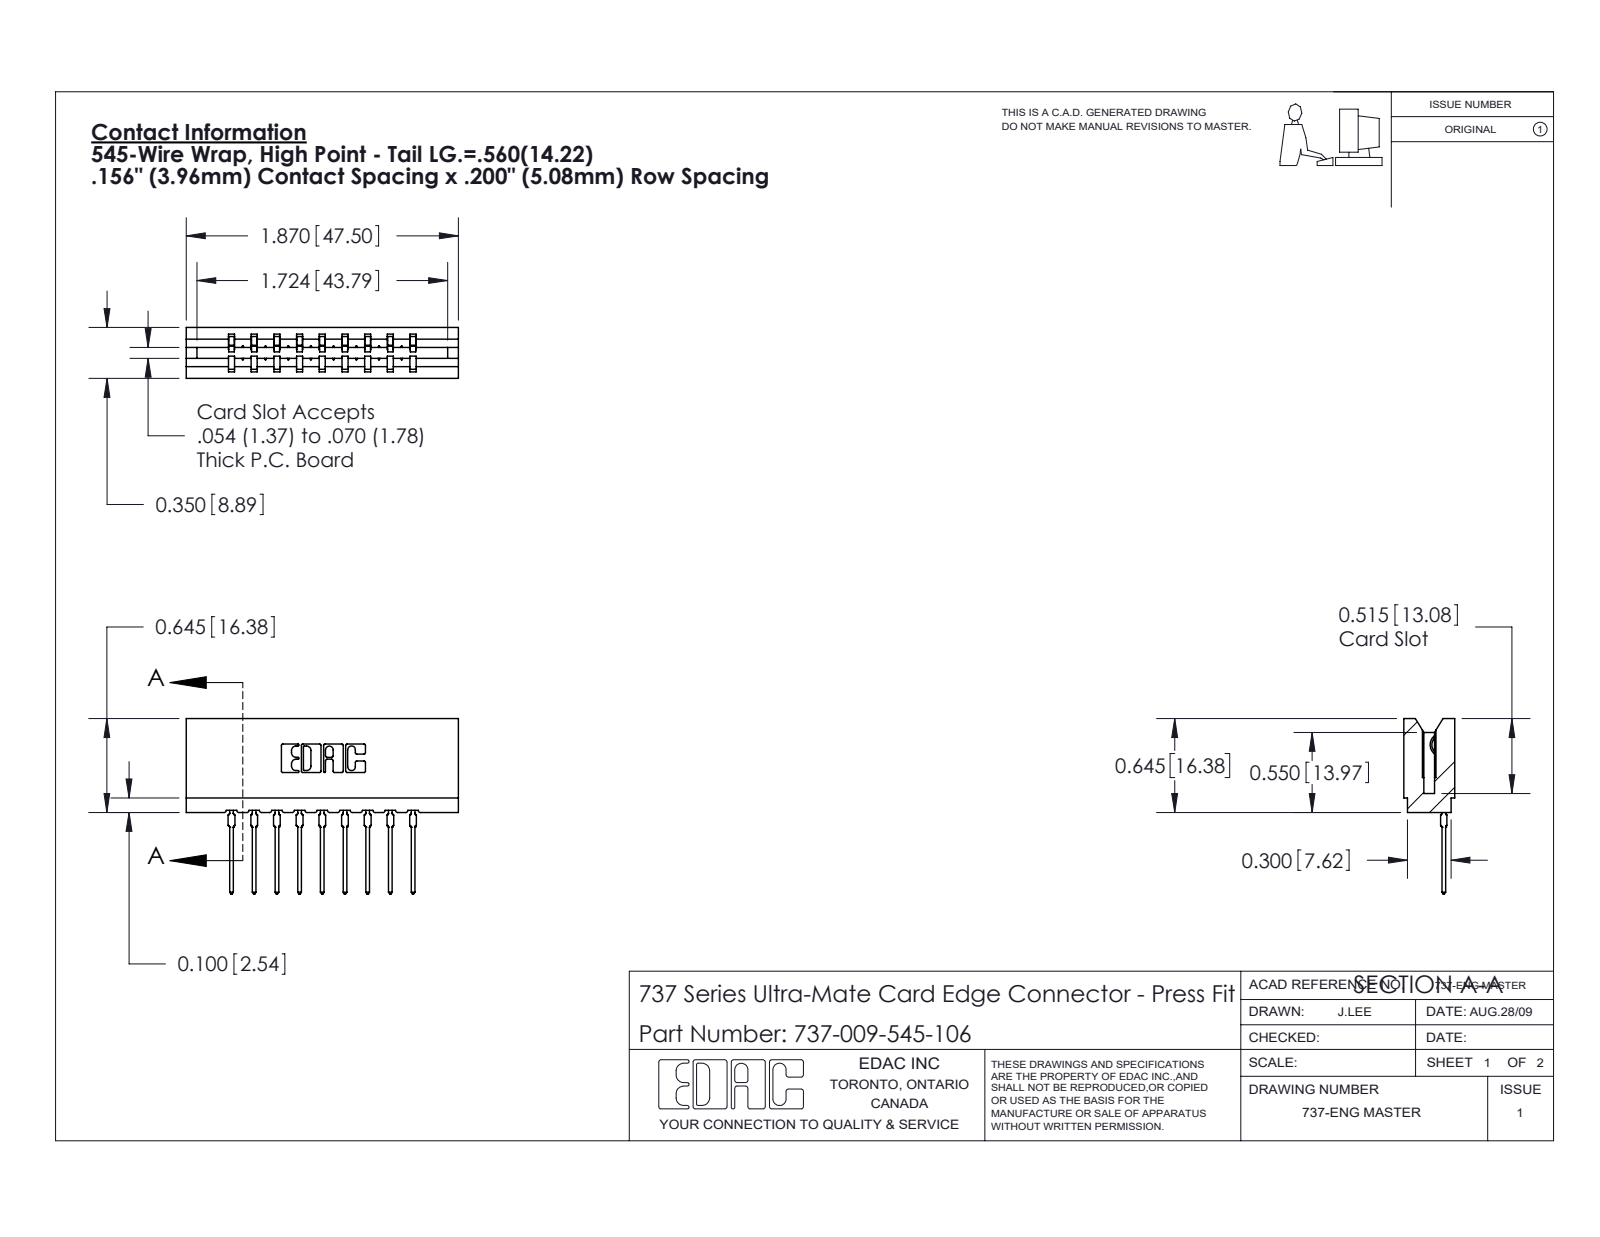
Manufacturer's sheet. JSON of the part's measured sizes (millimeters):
{"part_name": "745-292-001_545; 737 Part_Insulator Option - 06; 737-009-545-106", "step_written_by": "SolidWorks 2020 (CONFIG_CONTROL_DESIGN)", "units": "millimeters", "bodies": {"solids": 10, "faces": 1112, "planar": 667, "cylindrical": 211, "other": 234}, "overall_size": [47.5, 30.6, 8.9], "volume_mm3": 4830, "surface_area_mm2": 6027, "partial_cylinders_radius": [[0.3, 22], [0.4, 18], [0.5, 18], [0.2, 6], [0.8, 6], [0.1, 4], [0.3, 4], [0.7, 3]], "face_to_face_distances": [4, 3.5, 5.4, 15.8, 8.9, 7.9, 11.9, 9, 5, 19.8]}
